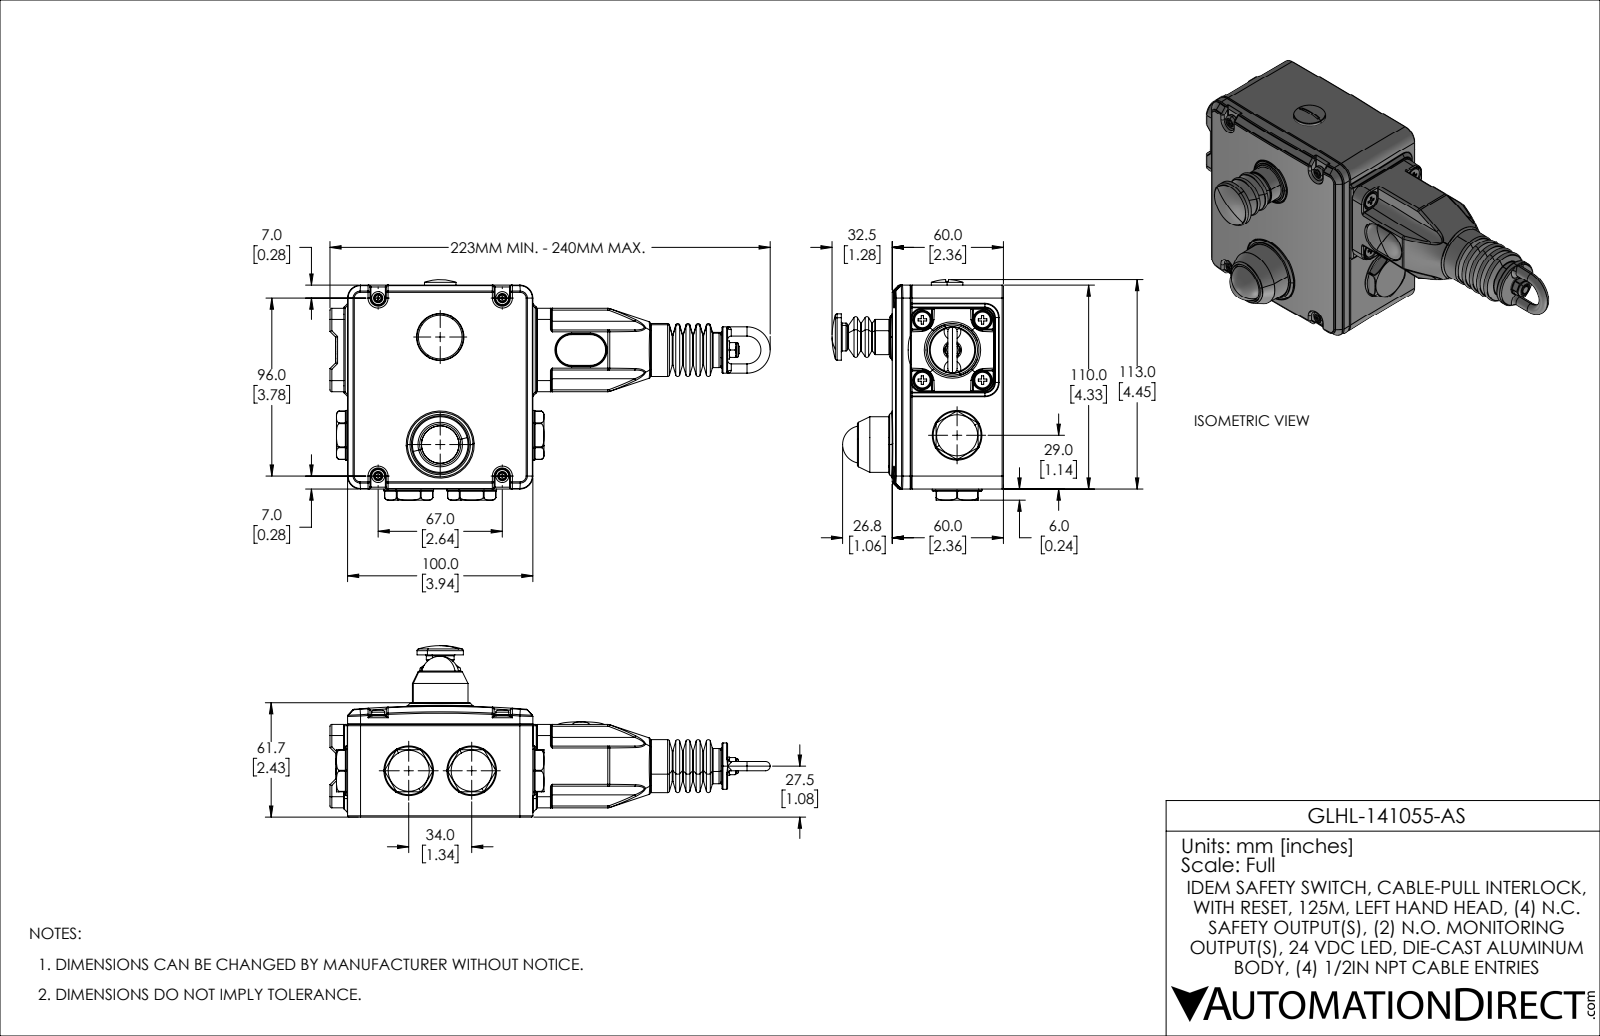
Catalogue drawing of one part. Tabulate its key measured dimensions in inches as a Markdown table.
| quantity | value |
| --- | --- |
| part name | GLHL-141055-AS |
| STEP written by | SolidWorks 2021 (AUTOMOTIVE_DESIGN) |
| units | inches |
| bodies | 41 solids, 4536 faces (1445 planar, 1448 cylindrical, 1643 other) |
| overall size | 9.354 × 4.685 × 3.642 |
| volume | 18.31 in³ |
| surface area | 285.5 in² |
| round holes (diameter × count) | 0.197 × 10, 0.209 × 9, 0.374 × 7, 0.354 × 5, 0.13 × 4, 0.157 × 4, 0.189 × 4, 0.213 × 4, 0.228 × 4, 0.067 × 3, 0.102 × 3, 0.118 × 3 |
| round bosses / shafts (diameter × count) | 0.335 × 7, 0.236 × 7, 0.173 × 7, 0.197 × 6, 0.276 × 5, 0.138 × 4, 0.051 × 4, 1.055 × 3 |
| partial cylindrical surfaces (radius × count) | 0.02 × 241, 0.039 × 157, 0.008 × 76, 0.028 × 72, 0.012 × 26, 0.006 × 14, 0.236 × 12, 0.004 × 10 |
| main face-to-face distances | 0.138, 2.157, 0.114, 2.043, 4.331, 0.055, 0.079, 0.157, 4.016, 3.878 |
| hole center spacings | 1.28, 0.228, 0.374, 0.905, 1.891, 1.913, 3.012, 3.489 |
